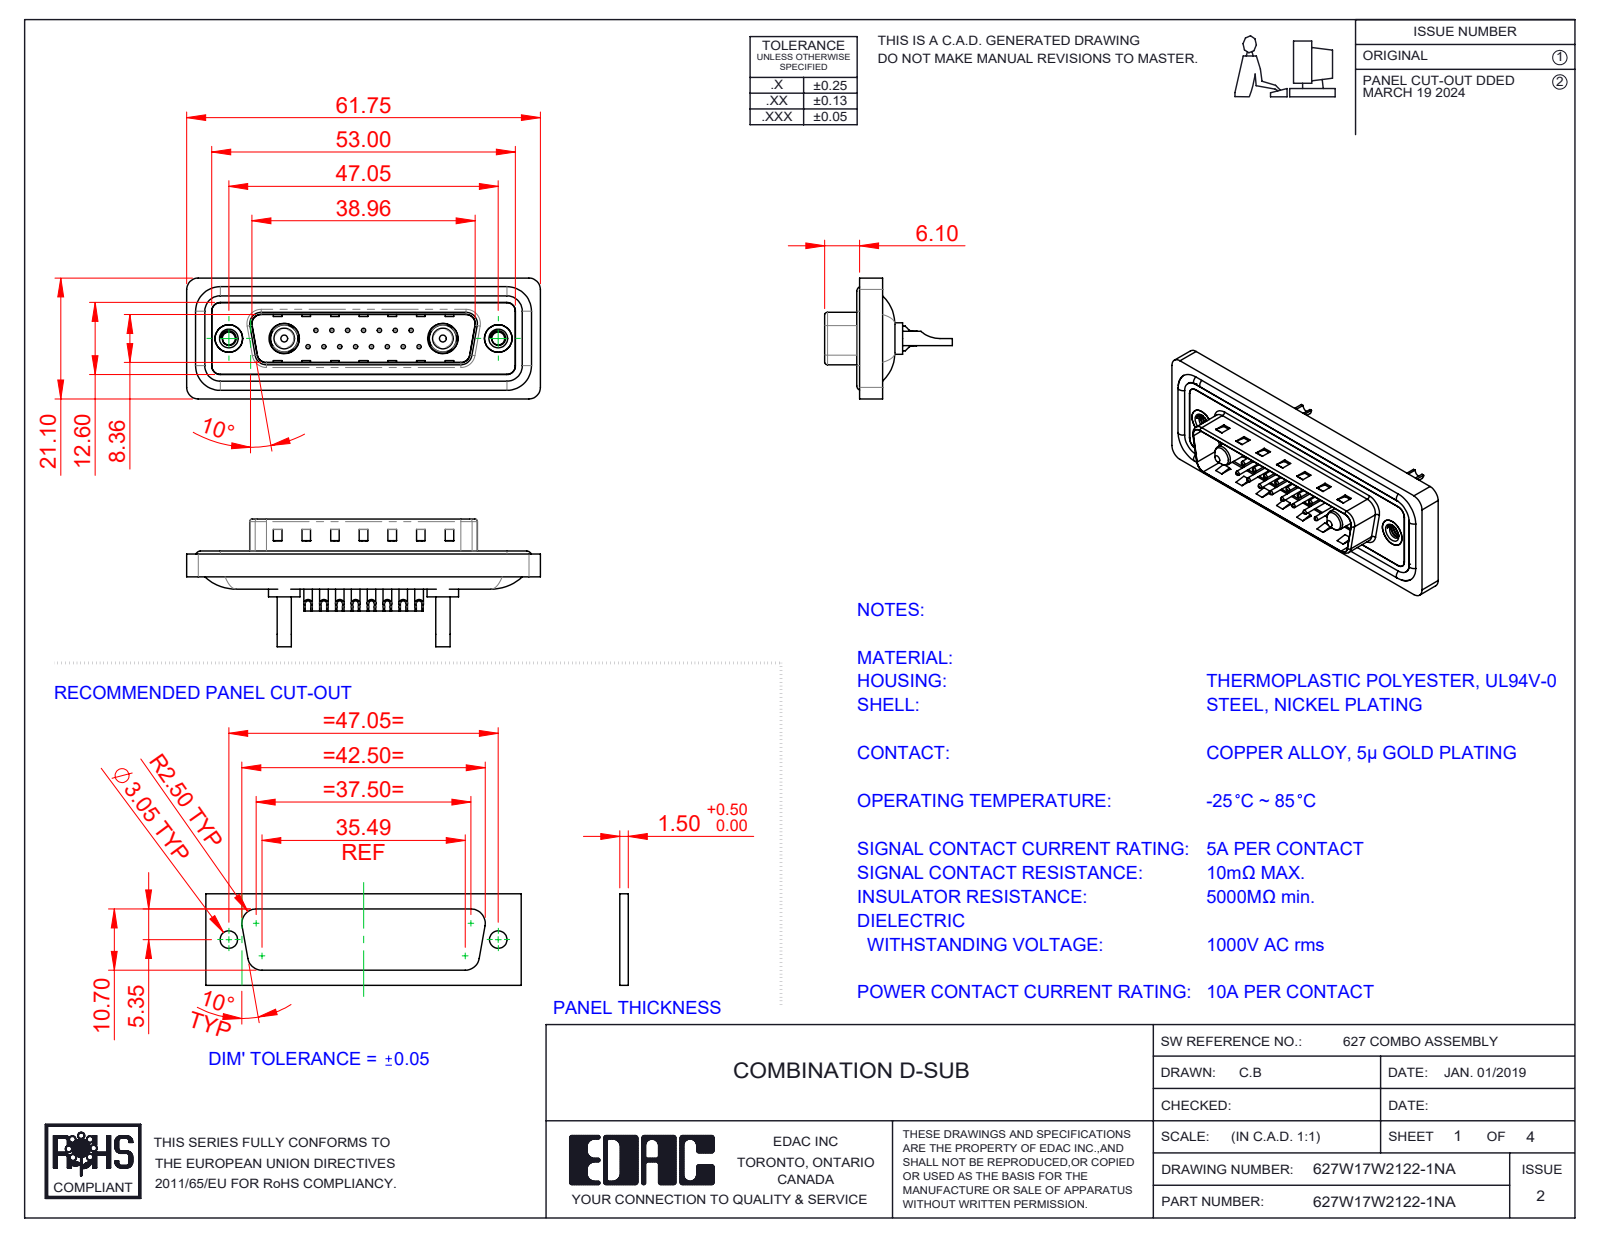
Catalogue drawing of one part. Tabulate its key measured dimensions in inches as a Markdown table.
| quantity | value |
| --- | --- |
| part name | 627Combo Shell Rear_25 Contacts; 627Combo Contact Row 2_22; 627W17W2122-1NA; 627Combo Waterproof Housing_25 Contacts (+5 more) |
| STEP written by | SolidWorks 2023 (CONFIG_CONTROL_DESIGN) |
| units | inches |
| bodies | 26 solids, 1124 faces (368 planar, 474 cylindrical, 282 other) |
| overall size | 2.431 × 0.878 × 0.831 |
| volume | 0.445 in³ |
| surface area | 18.8 in² |
| round holes (diameter × count) | 0.03 × 15, 0.039 × 15, 0.063 × 15, 0.079 × 15, 0.067 × 2, 0.089 × 2, 0.157 × 2, 0.189 × 2, 0.191 × 2, 0.197 × 2, 0.209 × 2 |
| round bosses / shafts (diameter × count) | 0.059 × 15, 0.063 × 4, 0.217 × 2, 0.205 × 2, 0.193 × 2, 0.187 × 2, 0.148 × 2, 0.142 × 2 |
| partial cylindrical surfaces (radius × count) | 0.059 × 22, 0.079 × 18, 0.02 × 8, 0.063 × 8, 0.039 × 6, 0.01 × 4, 0.024 × 4, 0.026 × 4 |
| main face-to-face distances | 0.016, 0.059, 0.043, 0.063, 0.02, 0.122, 0.114, 0.032, 0.377, 0.161 |
| hole center spacings | 0.124, 0.109, 0.218, 0.327, 0.198, 0.295, 0.436, 0.198 |
